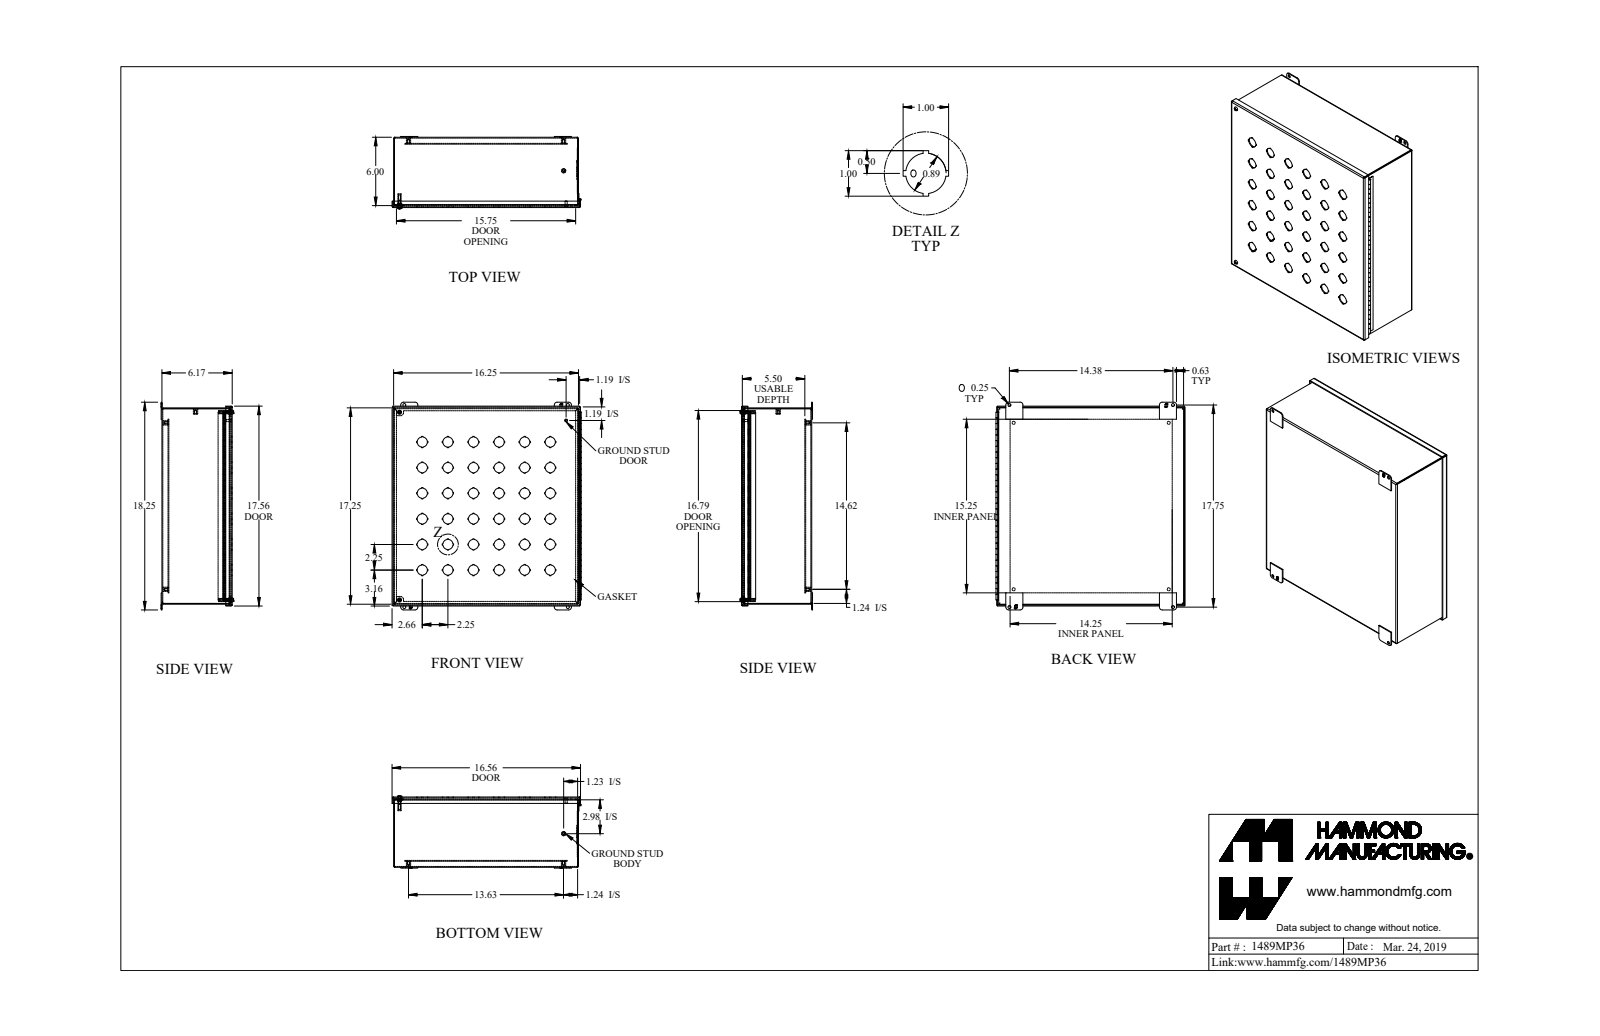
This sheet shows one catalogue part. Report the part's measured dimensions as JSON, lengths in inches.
{"part_name": "1489MP36_Default", "step_written_by": "SolidWorks 2019 (CONFIG_CONTROL_DESIGN)", "units": "inches", "bodies": {"solids": 21, "faces": 1373, "planar": 966, "cylindrical": 349, "other": 58}, "overall_size": [18.25, 16.623, 6.371], "volume_in3": 97.29, "surface_area_in2": 2621, "round_holes": [[0.886, 36], [0.25, 6], [0.156, 5], [0.265, 4], [0.159, 2], [0.406, 2]], "round_bosses_or_shafts": [[0.375, 5], [0.39, 2], [0.275, 2], [0.19, 2], [0.148, 2], [0.25, 1], [0.188, 1], [0.174, 1]], "partial_cylinders_radius": [[0.036, 12], [0.108, 12], [0.25, 8], [0.16, 2], [0.171, 2]], "face_to_face_distances": [0.072, 6.1, 5.568, 0.532, 6.028, 6.172, 0.604, 5.64, 0.46, 5.496], "hole_center_spacings": [5.031, 2.25, 7.115, 3.182, 4.5, 8.113, 6.75, 6.364]}
